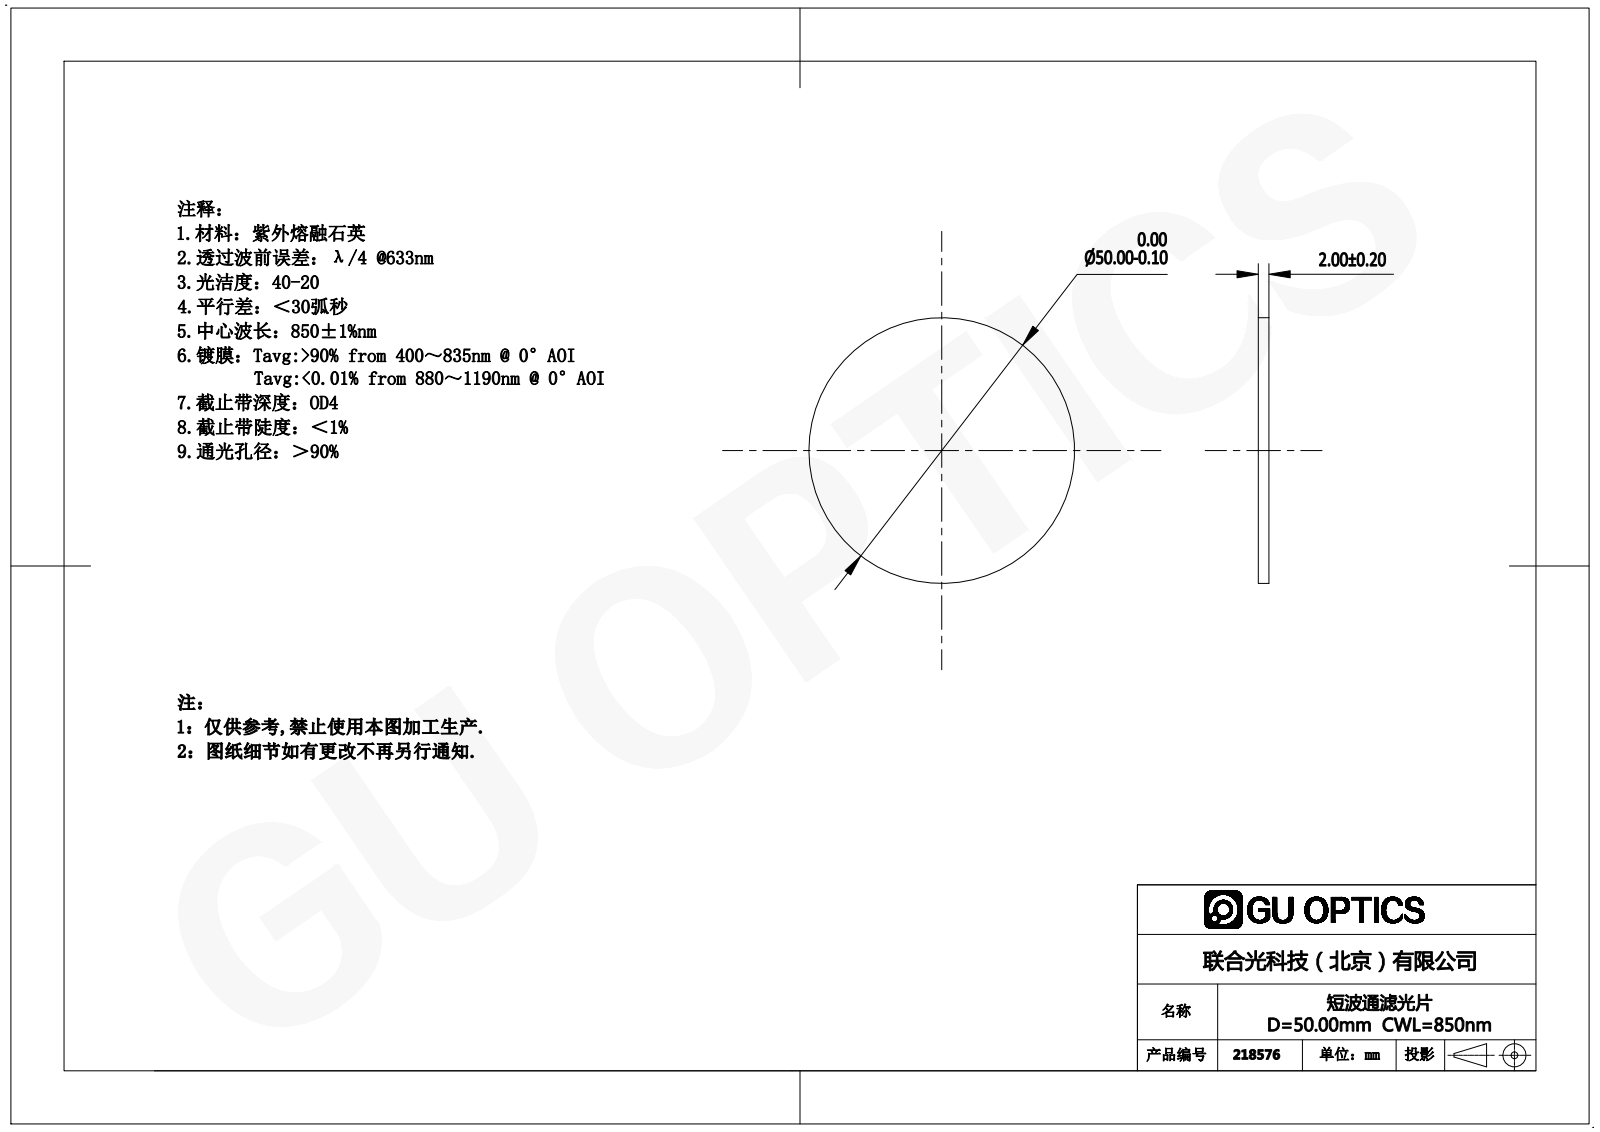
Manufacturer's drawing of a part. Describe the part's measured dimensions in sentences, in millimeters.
The part is named "218558". Its 3-D file was written by "SolidWorks 2016 (AUTOMOTIVE_DESIGN)". It is 1 solid with 4 faces: 2 planar, 2 cylindrical and 0 other. Overall it measures 50 by 50 by 2 millimeters. Its volume is 3 927 cubic millimeters and its surface area 4 241 square millimeters. Round bosses or shafts: 1 of diameter 50. The main face-to-face distances are 2.
